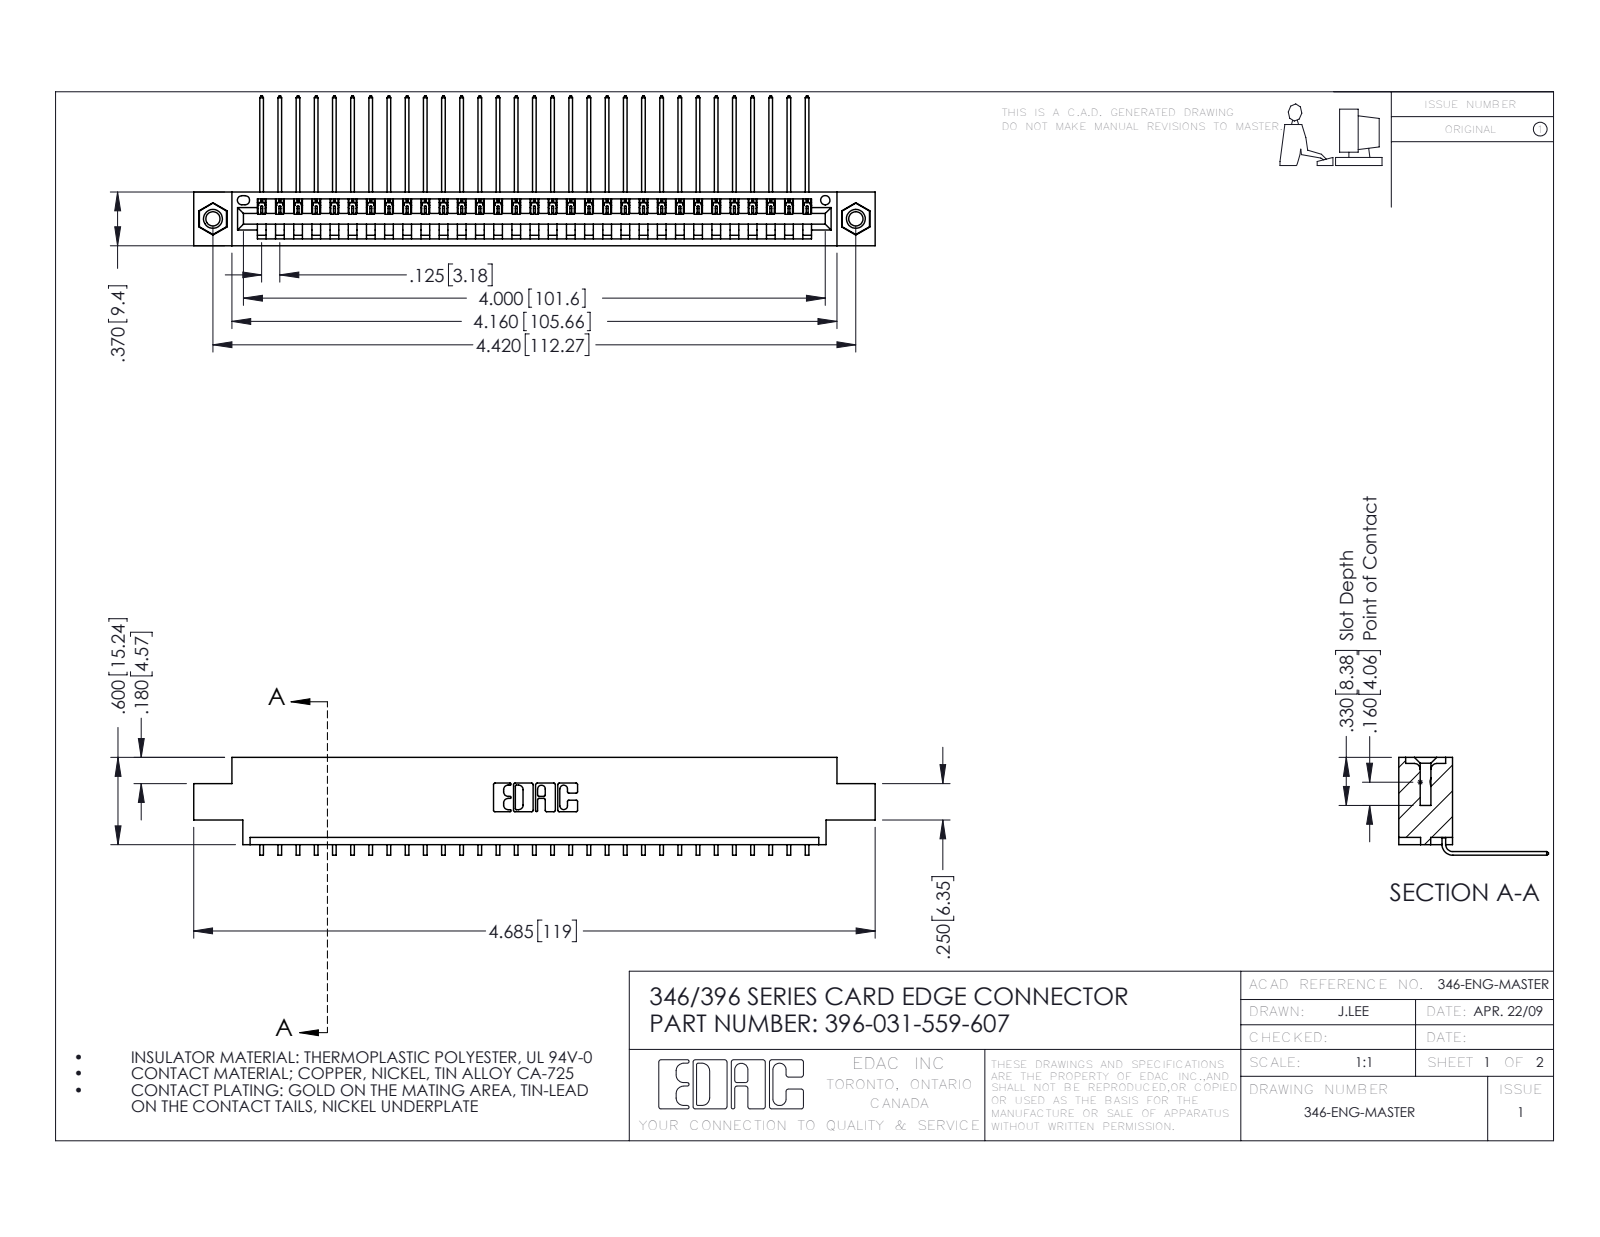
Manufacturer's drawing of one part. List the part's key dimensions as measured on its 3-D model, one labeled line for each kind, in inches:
Part name (STEP PRODUCT): 346 Part_0.170 Offset - 0.156 Dia-TI; 345-292-001_558 559 Tail - 1; 345-250-001_345-250-005-103; 396-031-559-607
STEP written by: SolidWorks 2016 (CONFIG_CONTROL_DESIGN)
Units: inches
Bodies: 34 solids, 2046 faces (1414 planar, 616 cylindrical, 16 other)
Overall size (bounding box): 4.685 × 1.03 × 0.673
Volume: 0.687 in³ · Surface area: 22.87 in²
Round holes (diameter × count): ⌀0.098 ×2, ⌀0.125 ×2, ⌀0.156 ×2, ⌀0.064 ×1
Round bosses / shafts (diameter × count): ⌀0.155 ×2
Partial cylindrical surfaces — rounded edges, fillets, slot ends (radius × count): R0.006 ×62, R0.01 ×22, R0.007 ×6, R0.031 ×6, R0.026 ×3, R0.031 ×2, R0.04 ×2, R0.014 ×1
Main face-to-face distances: 0.048, 0.322, 0.37, 0.25, 0.025, 0.072, 0.222, 0.148, 0.298, 0.1
Hole centre spacings: 0.246, 4.212, 4.42
